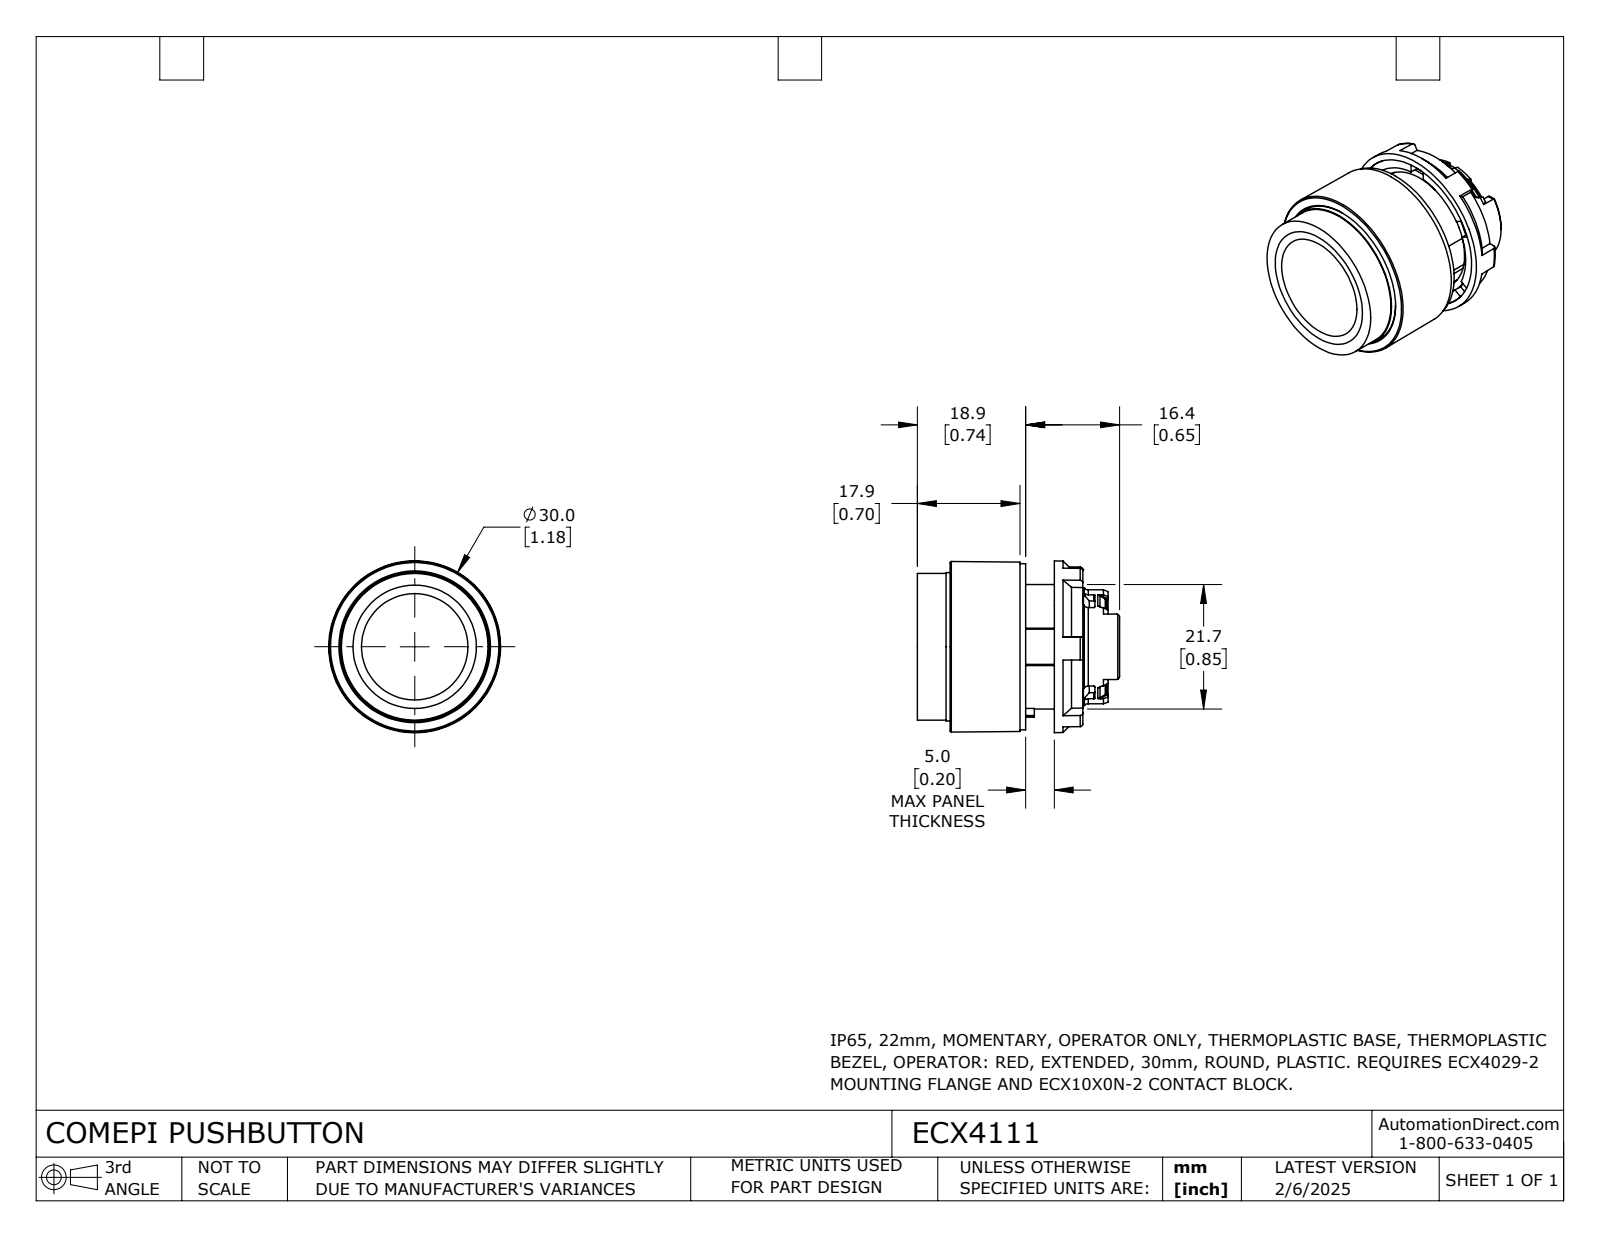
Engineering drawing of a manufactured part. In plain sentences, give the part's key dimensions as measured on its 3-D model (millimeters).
The part is named "ECX4111". Its 3-D file was written by "SolidWorks 2024 (CONFIG_CONTROL_DESIGN)". It is 3 solids with 401 faces: 135 planar, 113 cylindrical and 153 other. Overall it measures 35.3 by 30 by 30 millimeters. Its volume is 10 800 cubic millimeters and its surface area 11 140 square millimeters. Round holes: 1 of diameter 13.5, 1 of diameter 18.1, 1 of diameter 22.1. Round bosses or shafts: 1 of diameter 29, 1 of diameter 25.9, 1 of diameter 25.6, 1 of diameter 24.5, 1 of diameter 21.7, 1 of diameter 20.5, 1 of diameter 20, 1 of diameter 19. Partial cylindrical surfaces (rounded edges, fillets, slot ends): 24 of radius 0.2, 8 of radius 0.5, 2 of radius 0.3, 1 of radius 7.4, 1 of radius 8.7, 1 of radius 8.8, 1 of radius 9.3. The main face-to-face distances are 10.4, 1, 11, 6, 5, 11.4, 5.5, 5.9, 15.5, 4.5.
